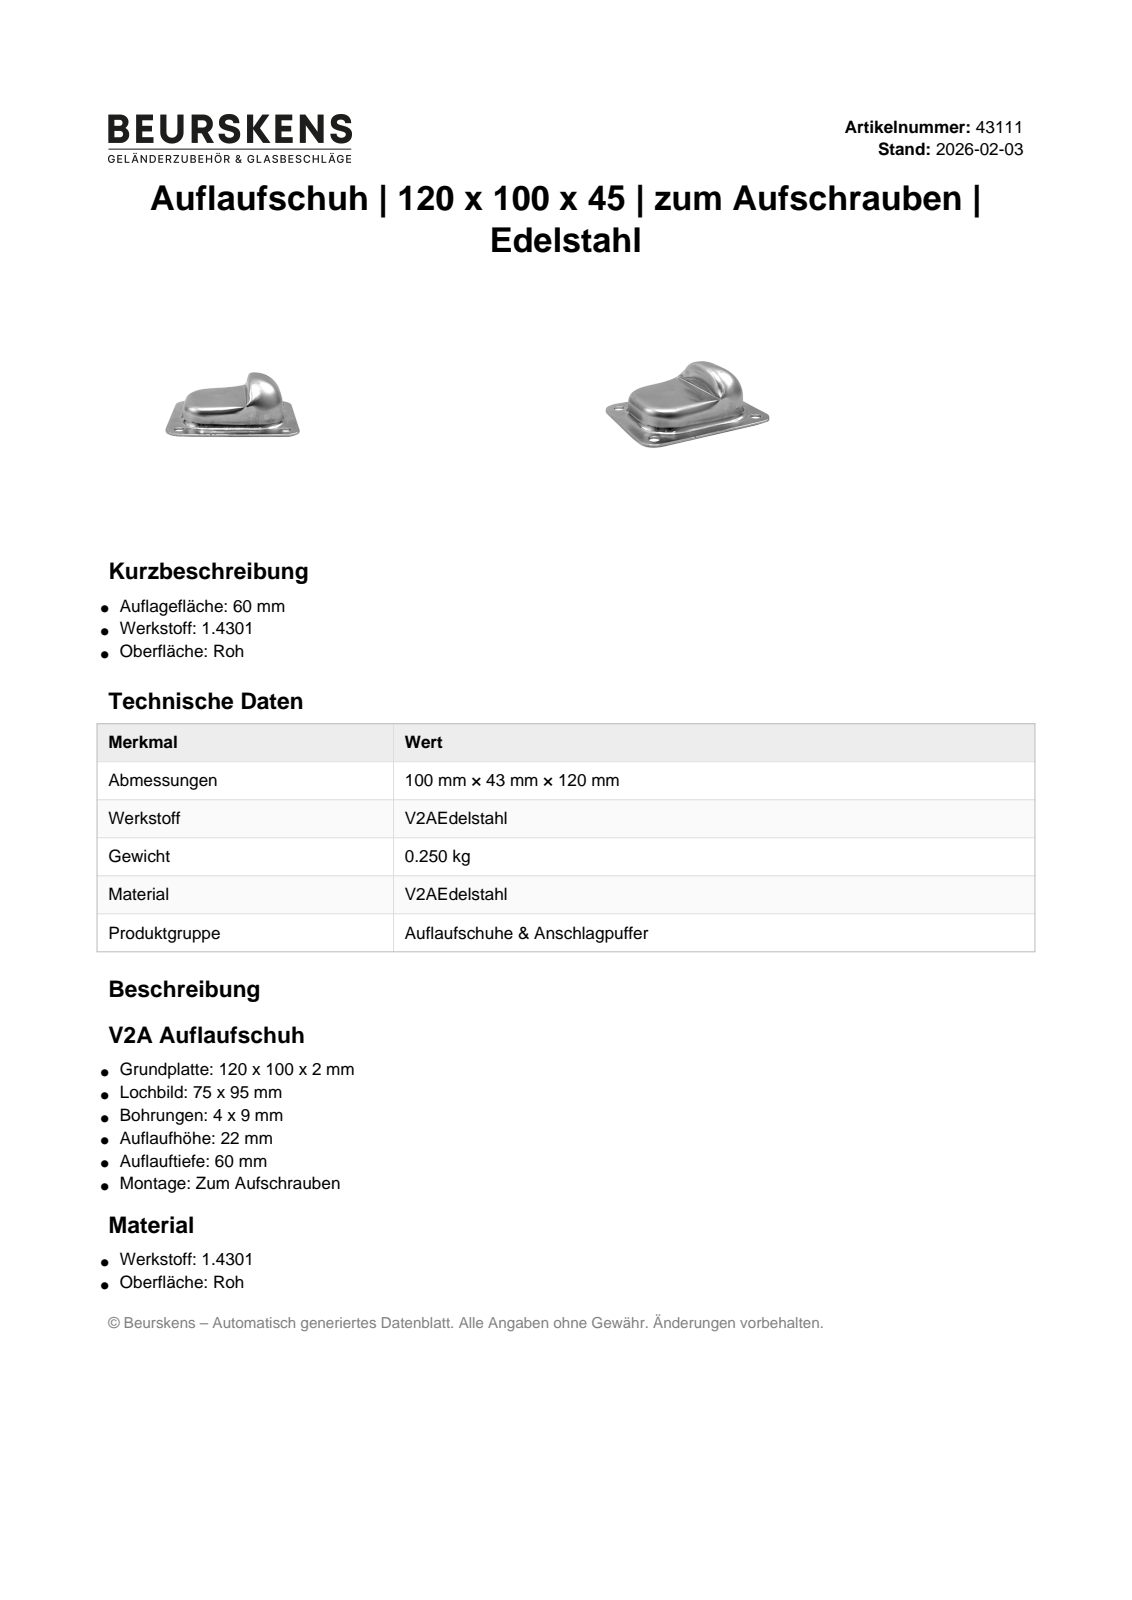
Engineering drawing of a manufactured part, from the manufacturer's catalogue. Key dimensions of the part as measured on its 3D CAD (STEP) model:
Part name (STEP PRODUCT): 43111
STEP written by: Autodesk Inventor 2022 (AUTOMOTIVE_DESIGN)
Units: millimetres
Bodies: 1 solid, 82 faces (20 planar, 42 cylindrical, 20 other)
Overall size (bounding box): 120 × 100 × 46
Volume: 40 014 mm³ · Surface area: 41 091 mm²
Round holes (diameter × count): ⌀9 ×4
Partial cylindrical surfaces — rounded edges, fillets, slot ends (radius × count): R5.5 ×9, R7.5 ×9, R1.25 ×4, R3.25 ×4, R8 ×4, R15.5 ×3, R17.5 ×3, R19.25 ×1
Main face-to-face distances: 2, 22, 20, 24, 68, 28, 70, 66, 26, 30
Hole centre spacings: 75, 95, 121.04
